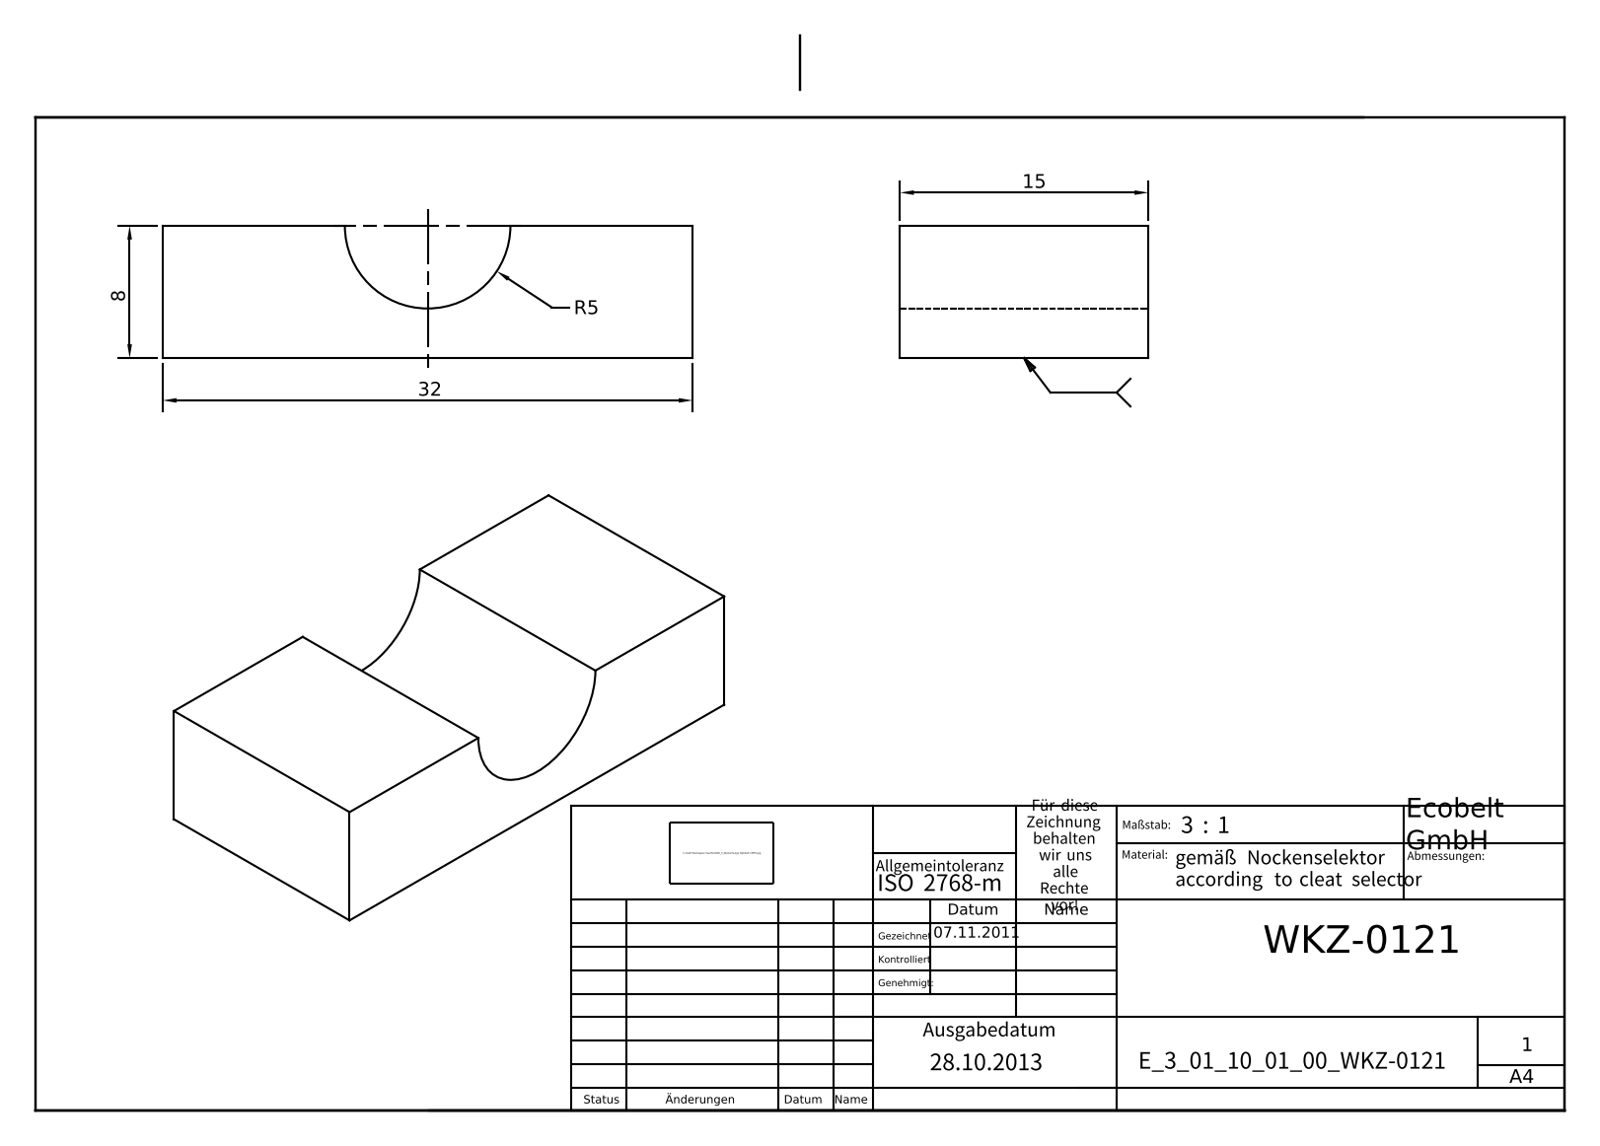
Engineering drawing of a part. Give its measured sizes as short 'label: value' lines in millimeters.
name: E_3_01_10_01_00_WKZ-0121
written by: Autodesk Inventor 2025 (AUTOMOTIVE_DESIGN)
unit: mm
bodies: 1 solid, 8 faces (7 planar, 1 cylindrical, 0 other)
size: 32 × 15 × 8
volume: 3 251 mm³; area: 1 719 mm²
rounds: 1× R5
face distances: 8, 15, 32
